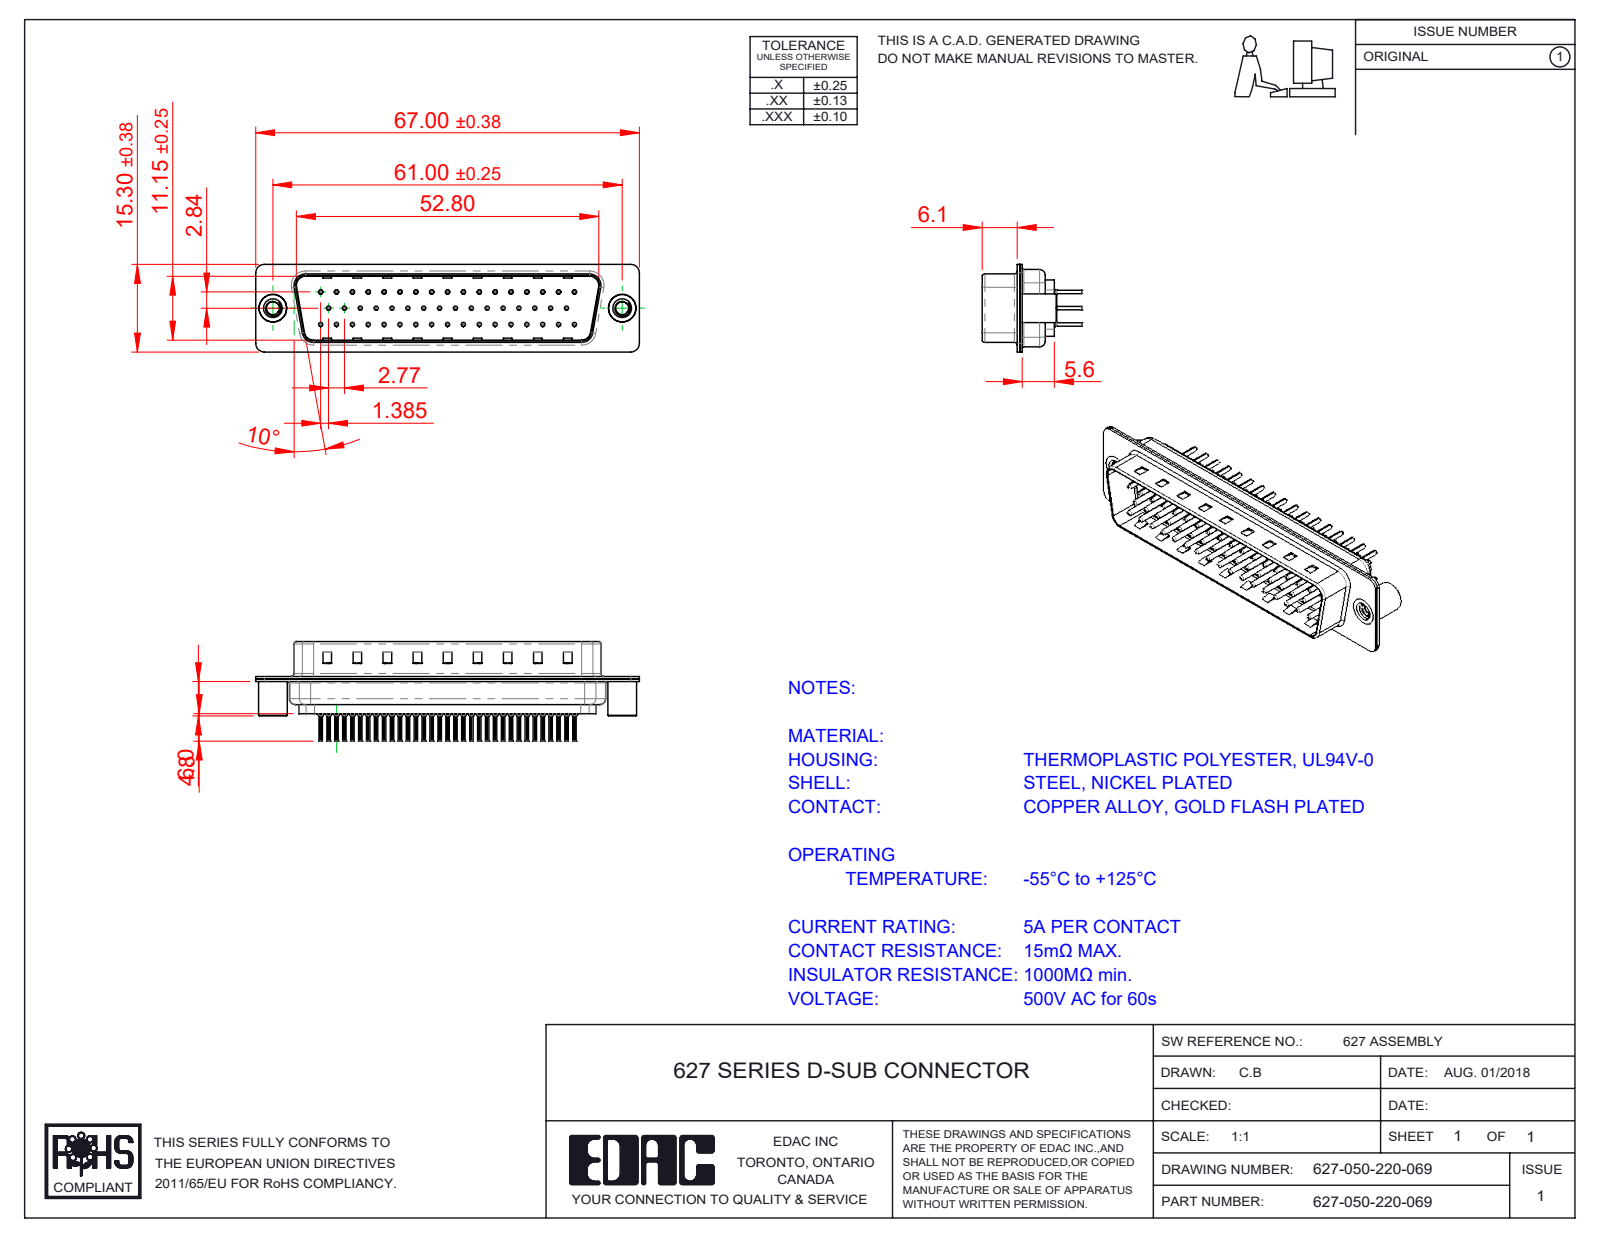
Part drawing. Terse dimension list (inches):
name: 627 Contact Row 3_20L; 627 Housing_50 LP; 627 Shell Front_50 Contacts; 627 Shell Rear_50 Contacts (+4 more)
written by: SolidWorks 2020 (CONFIG_CONTROL_DESIGN)
unit: in
bodies: 55 solids, 5334 faces (1403 planar, 2011 cylindrical, 1920 other)
size: 2.638 × 0.681 × 0.602
volume: 0.276 in³; area: 19.8 in²
holes: 50× ⌀0.008, 50× ⌀0.014, 50× ⌀0.043, 50× ⌀0.063, 2× ⌀0.089, 2× ⌀0.157, 2× ⌀0.189
bosses: 50× ⌀0.079, 50× ⌀0.059, 50× ⌀0.03, 50× ⌀0.024, 2× ⌀0.197, 2× ⌀0.193
rounds: 100× R0.004, 16× R0.059, 12× R0.079, 8× R0.02, 8× R0.063, 4× R0.01, 4× R0.024, 4× R0.026
face distances: 0.016, 0.018, 0.455, 0.035, 0.238, 0.256, 0.031, 0.485, 0.077, 0.03
hole spacings: 0.124, 0.109, 0.218, 0.327, 0.436, 0.545, 0.654, 0.198
